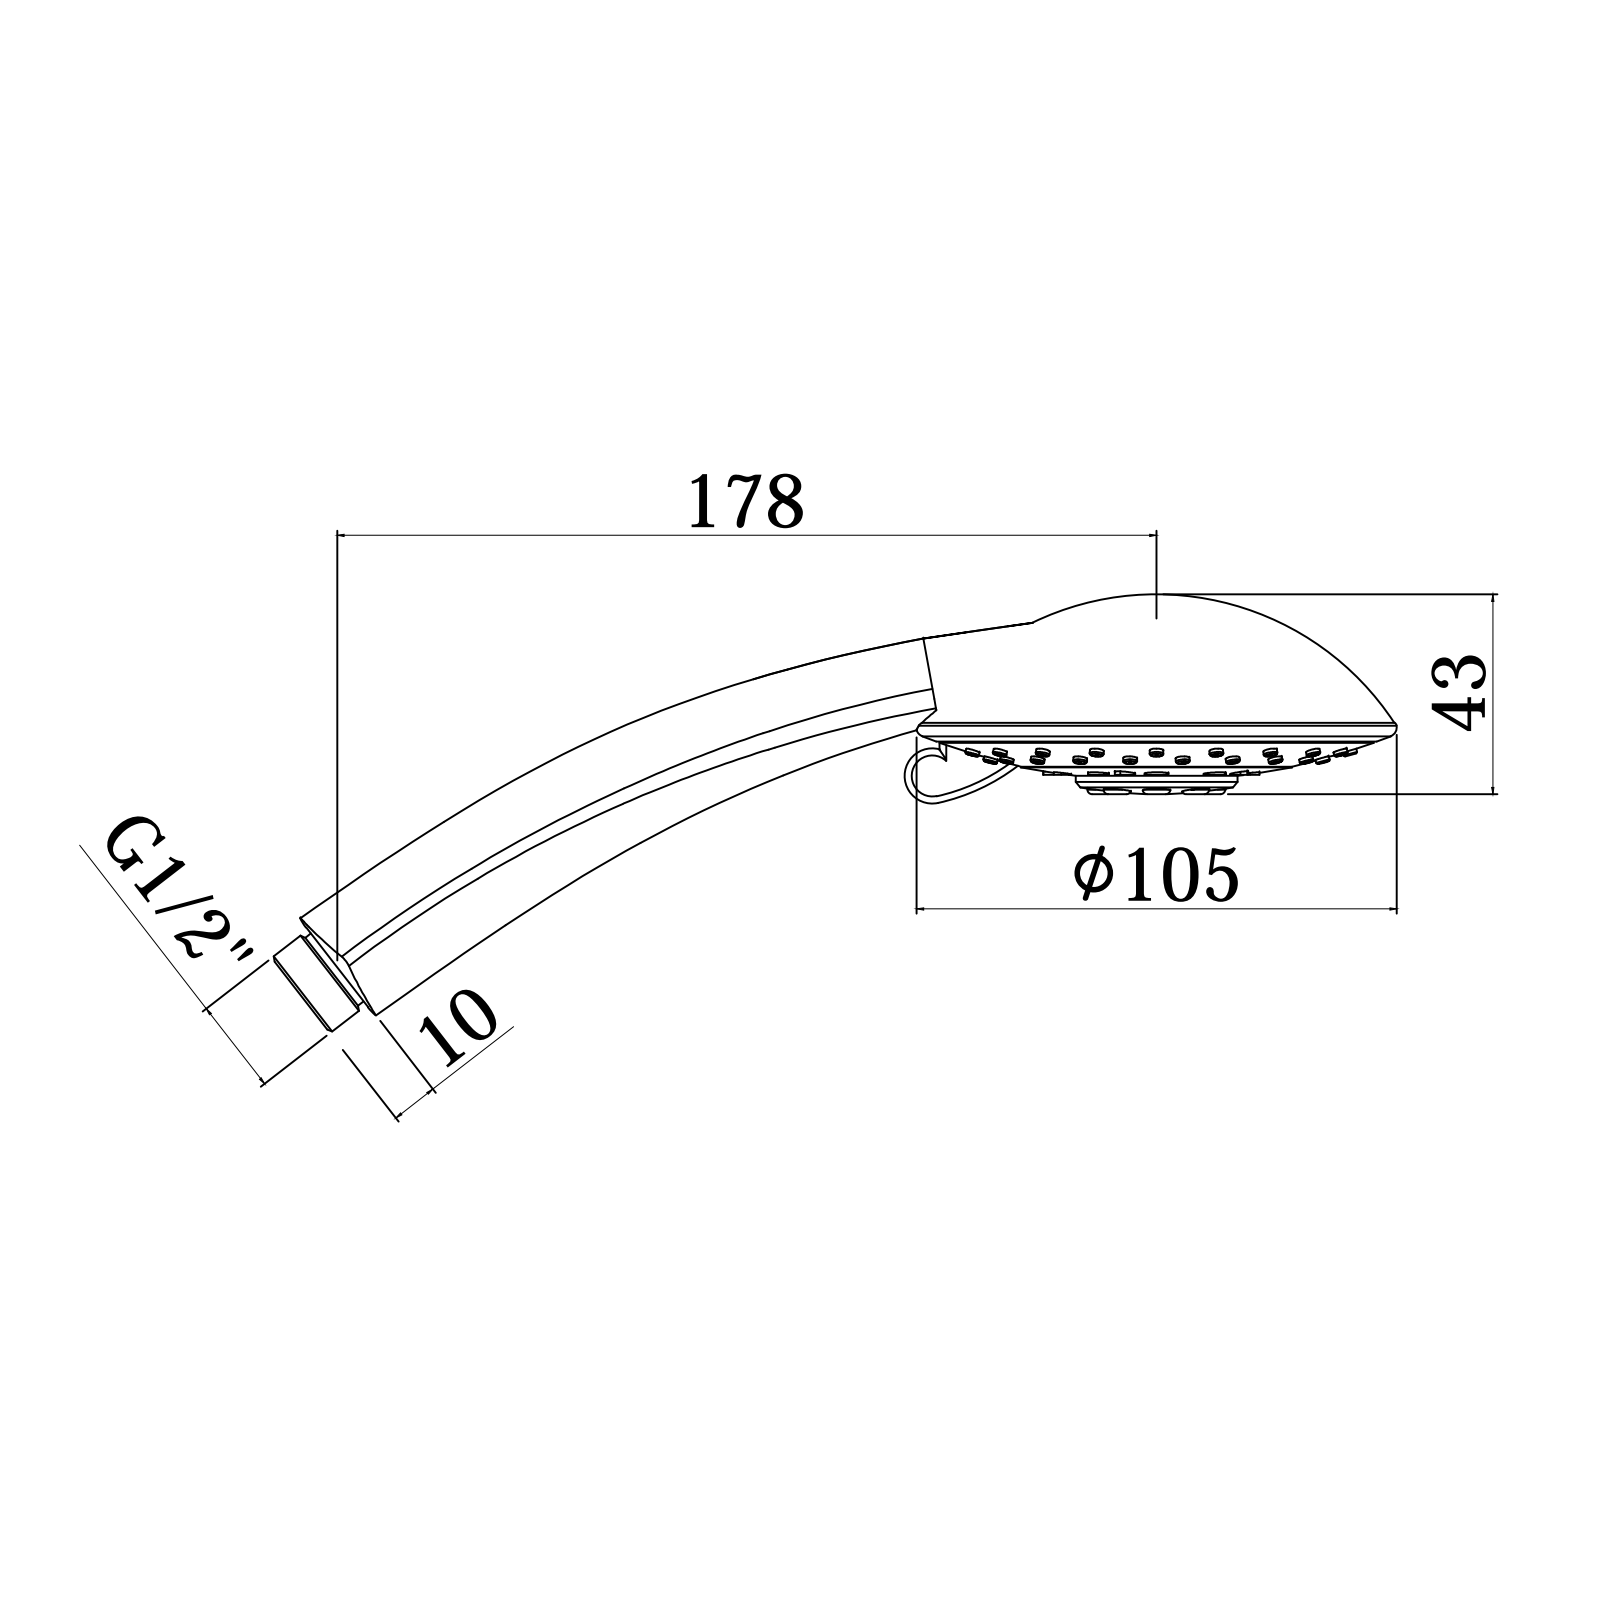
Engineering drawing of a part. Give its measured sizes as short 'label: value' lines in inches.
name: ZDOC075CR
written by: CREO PARAMETRIC BY PTC INC, 2020044 (CONFIG_CONTROL_DESIGN)
unit: in
bodies: 2 solids, 573 faces (81 planar, 289 cylindrical, 203 other)
size: 9.615 × 4.114 × 3.744
volume: 17.46 in³; area: 78.94 in²
holes: 39× ⌀0.02, 15× ⌀0.055, 8× ⌀0.051, 1× ⌀0.433, 1× ⌀0.512, 1× ⌀0.551
bosses: 39× ⌀0.118, 1× ⌀2.323, 1× ⌀1.386, 1× ⌀0.815, 1× ⌀0.736
rounds: 30× R0.049, 30× R0.121, 8× R0.118, 2× R0.059, 1× R0.235, 1× R1.744, 1× R7.874
face distances: 0.276, 0.285, 0.157, 0.165, 0.441, 0.451, 0.392, 0.354, 0.037, 0.079
hole spacings: 0.333, 1.699, 0.27, 0.333, 0.362, 0.523, 0.781, 0.873
